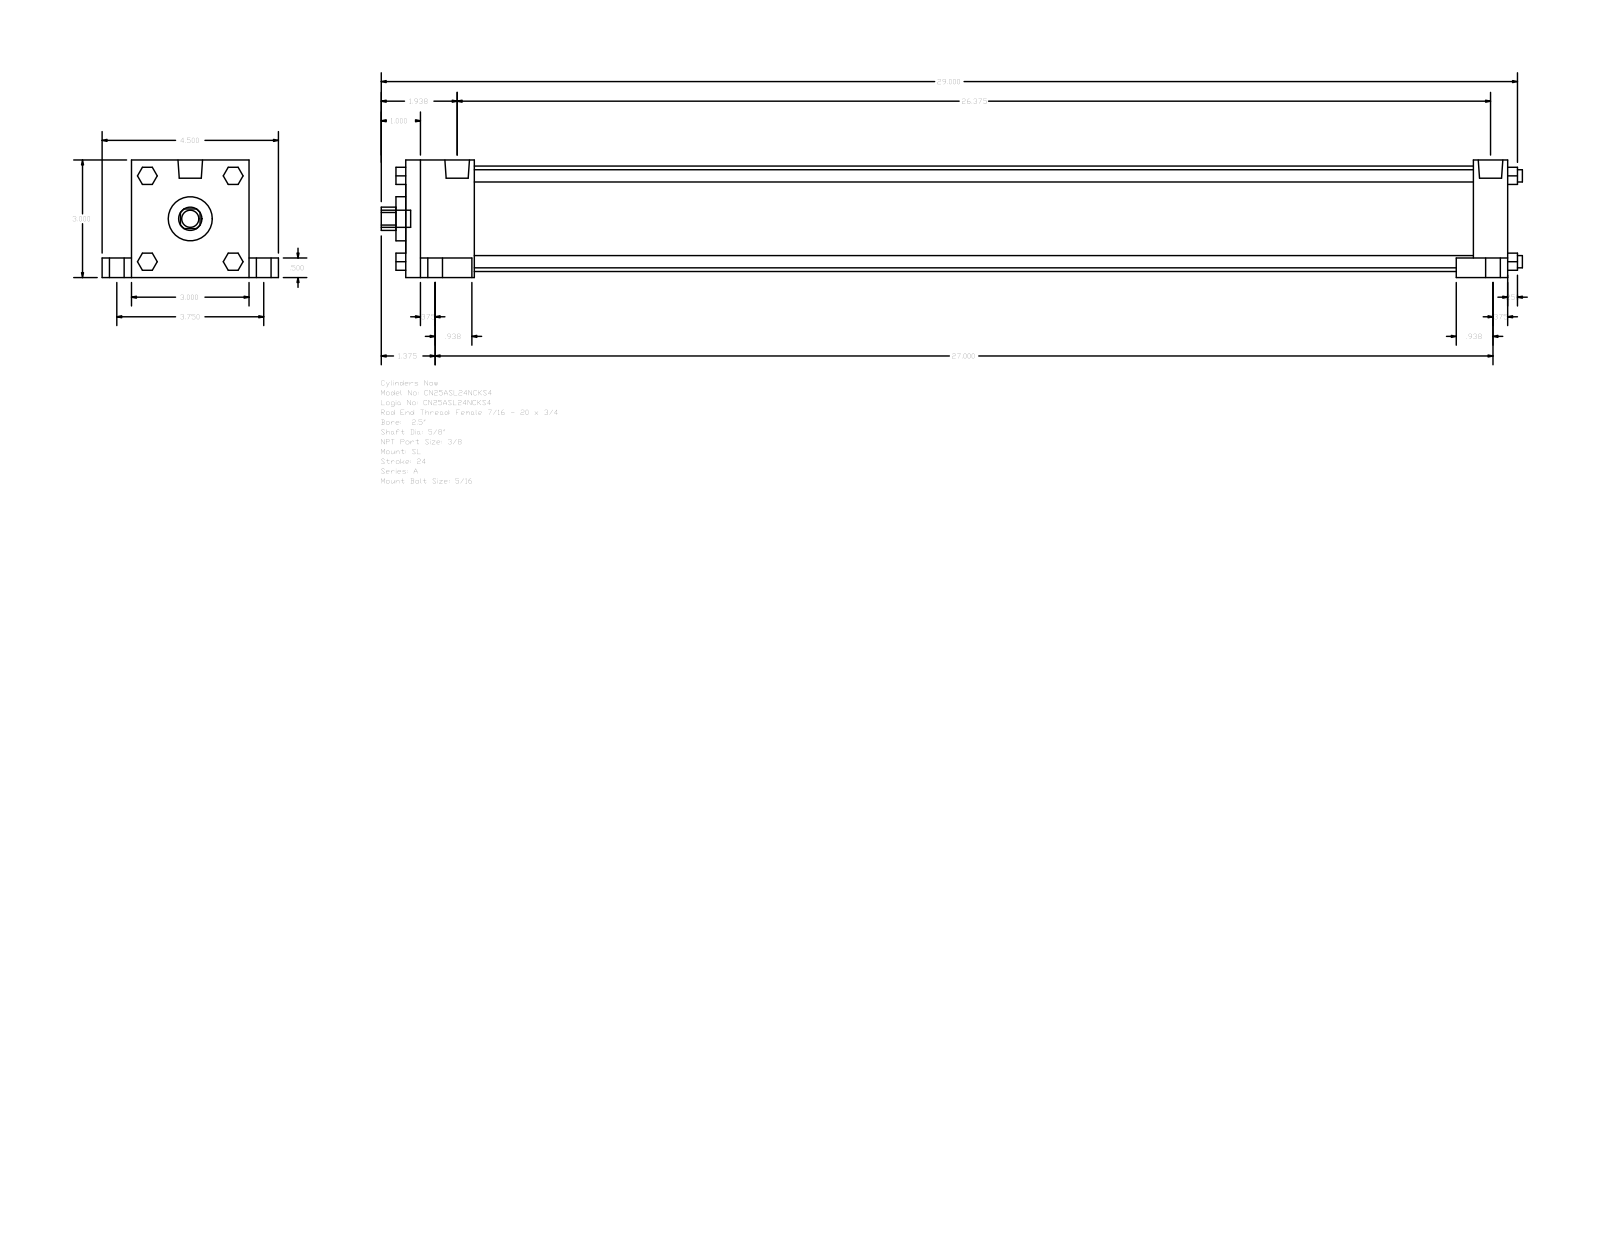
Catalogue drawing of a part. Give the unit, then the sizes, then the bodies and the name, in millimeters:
Units: millimetres
Overall size (bounding box): 739.77 × 114.3 × 76.2
Round holes (diameter × count): ⌀15.88 ×1, ⌀28.57 ×1, ⌀68.33 ×1
Round bosses / shafts (diameter × count): ⌀15.88 ×4, ⌀9.53 ×4, ⌀7.94 ×4, ⌀5.56 ×4, ⌀15.93 ×2, ⌀11.11 ×1
Partial cylindrical surfaces — rounded edges, fillets, slot ends (radius × count): R7.54 ×1
Main face-to-face distances: 76.2, 714.37, 44.45, 669.92, 692.14, 647.69, 22.23, 12.7, 63.5, 19.05
Bodies: 0 solids, 148 faces (112 planar, 36 cylindrical, 0 other)
Part name (STEP PRODUCT): A_SL__0250_0.625
STEP written by: GSSL Pune (CONFIG_CONTROL_DESIGN)
